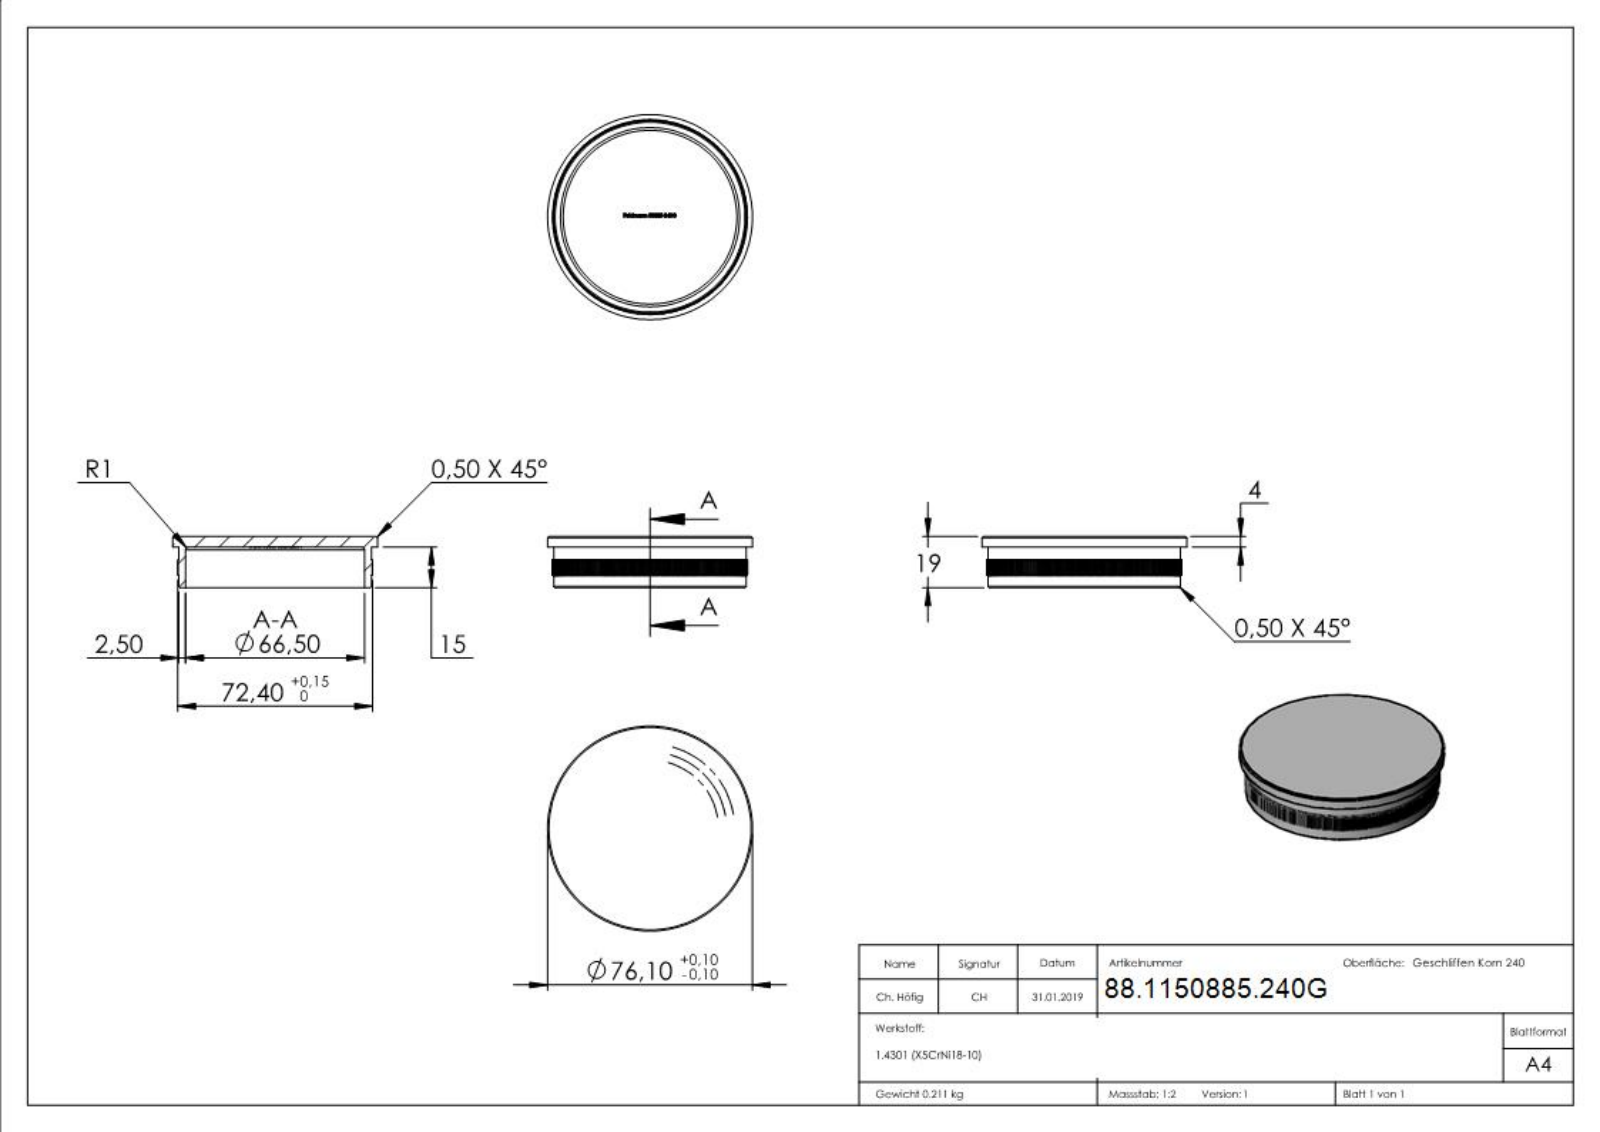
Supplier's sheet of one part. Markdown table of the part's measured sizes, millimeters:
| quantity | value |
| --- | --- |
| part name | 50885-240G |
| STEP written by | SolidWorks 2015 (CONFIG_CONTROL_DESIGN) |
| units | millimeters |
| bodies | 1 solid, 2792 faces (1565 planar, 368 cylindrical, 859 other) |
| overall size | 76.1 × 76.1 × 19 |
| volume | 26 652 mm³ |
| surface area | 17 472 mm² |
| round holes (diameter × count) | 66.5 × 1 |
| round bosses / shafts (diameter × count) | 76.1 × 1, 71.5 × 1 |
| partial cylindrical surfaces (radius × count) | 36.2 × 1 |
| main face-to-face distances | 4, 35.74, 35.76, 15, 19, 4.5, 10.5, 35.72, 35.78, 14.5 |
